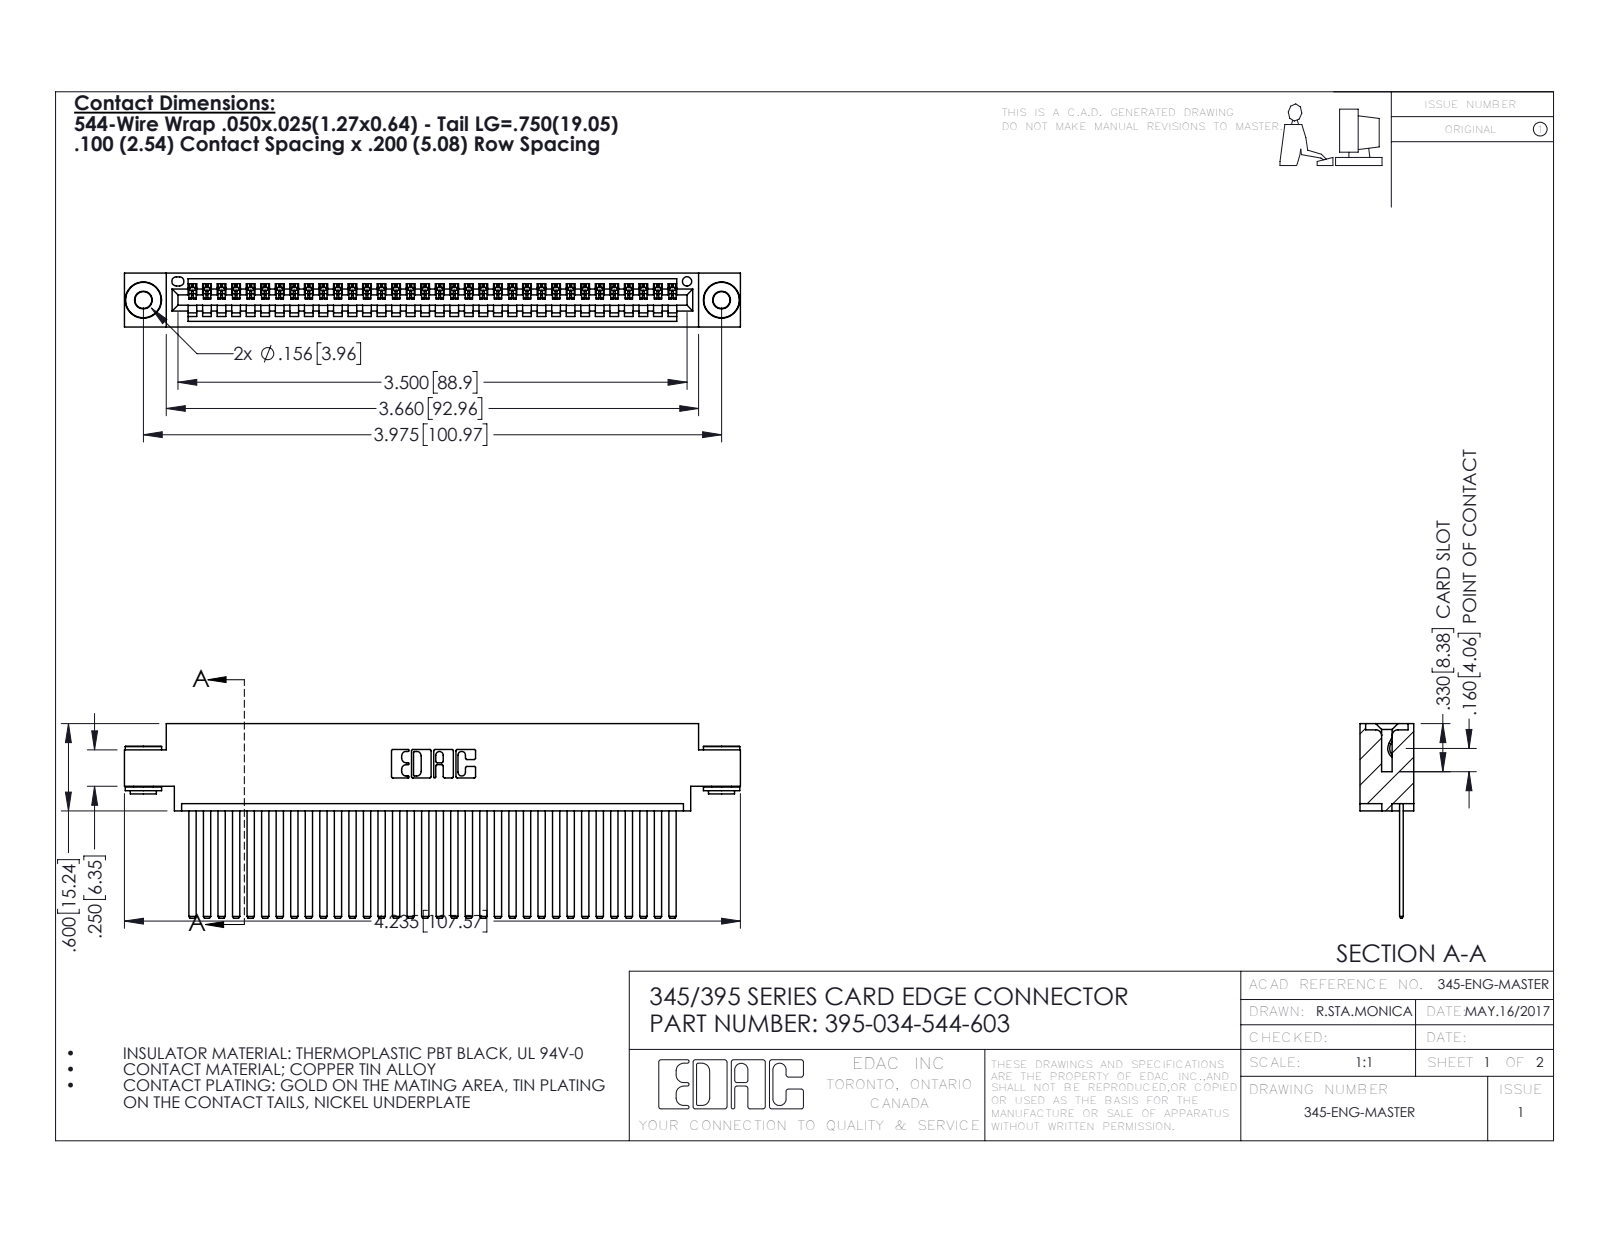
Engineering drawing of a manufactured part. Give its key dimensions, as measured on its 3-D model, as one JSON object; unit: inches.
{"part_name": "345-250-002_345-250-002-102; 345-292-001_345-293-144; 395-034-544-603; 345 Part_0.170 Offset - 0.156 Dia-TH", "step_written_by": "SolidWorks 2016 (CONFIG_CONTROL_DESIGN)", "units": "inches", "bodies": {"solids": 37, "faces": 1936, "planar": 1318, "cylindrical": 610, "other": 8}, "overall_size": [4.235, 1.337, 0.37], "volume_in3": 0.638, "surface_area_in2": 23.72, "round_holes": [[0.116, 2], [0.156, 2], [0.064, 1]], "round_bosses_or_shafts": [[0.25, 2], [0.18, 2], [0.136, 2]], "partial_cylinders_radius": [[0.006, 68], [0.01, 22], [0.007, 6], [0.031, 6], [0.026, 3], [0.031, 2], [0.04, 2], [0.014, 1]], "face_to_face_distances": [0.072, 0.298, 0.025, 0.098, 0.272, 0.37, 0.2, 0.225, 0.175, 0.149], "hole_center_spacings": [0.27, 3.74, 3.975]}
